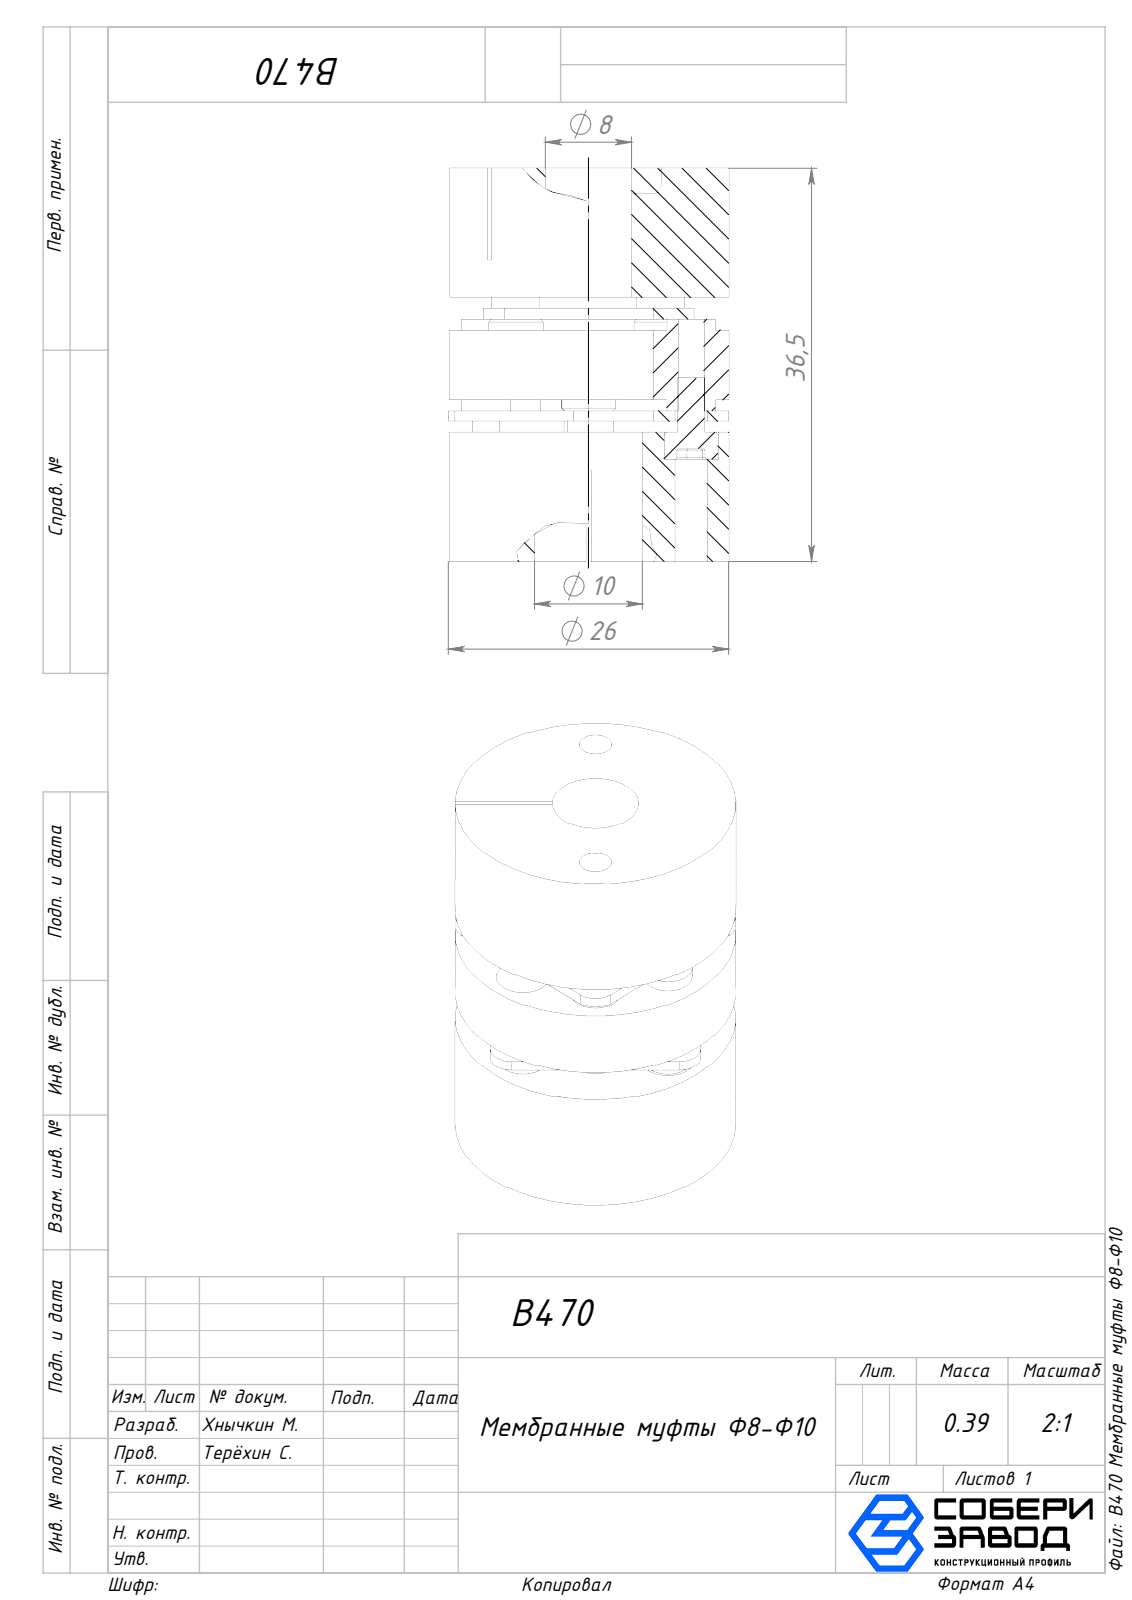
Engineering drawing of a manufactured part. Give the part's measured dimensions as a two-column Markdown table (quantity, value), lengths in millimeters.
| quantity | value |
| --- | --- |
| part name | Верх_00; Ниж.часть_00; Винт_00; Средняя часть_00 (+1 more) |
| STEP written by | SolidWorks 2025 (AUTOMOTIVE_DESIGN) |
| units | millimeters |
| bodies | 11 solids, 362 faces (120 planar, 226 cylindrical, 16 other) |
| overall size | 36.5 × 26 × 26 |
| volume | 13 815 mm³ |
| surface area | 9 774 mm² |
| round holes (diameter × count) | 3 × 8, 5 × 8, 2.4 × 4, 8 × 1, 10 × 1, 12 × 1 |
| round bosses / shafts (diameter × count) | 4.5 × 8, 2.5 × 8, 26 × 1 |
| partial cylindrical surfaces (radius × count) | 0.1 × 48, 0.25 × 48, 2 × 8 |
| main face-to-face distances | 1, 9.5, 2, 12, 10.5, 24.5, 14, 8.5, 15, 3 |
| hole center spacings | 7.27, 9.5, 13.44, 17.56, 19, 19.01 |
